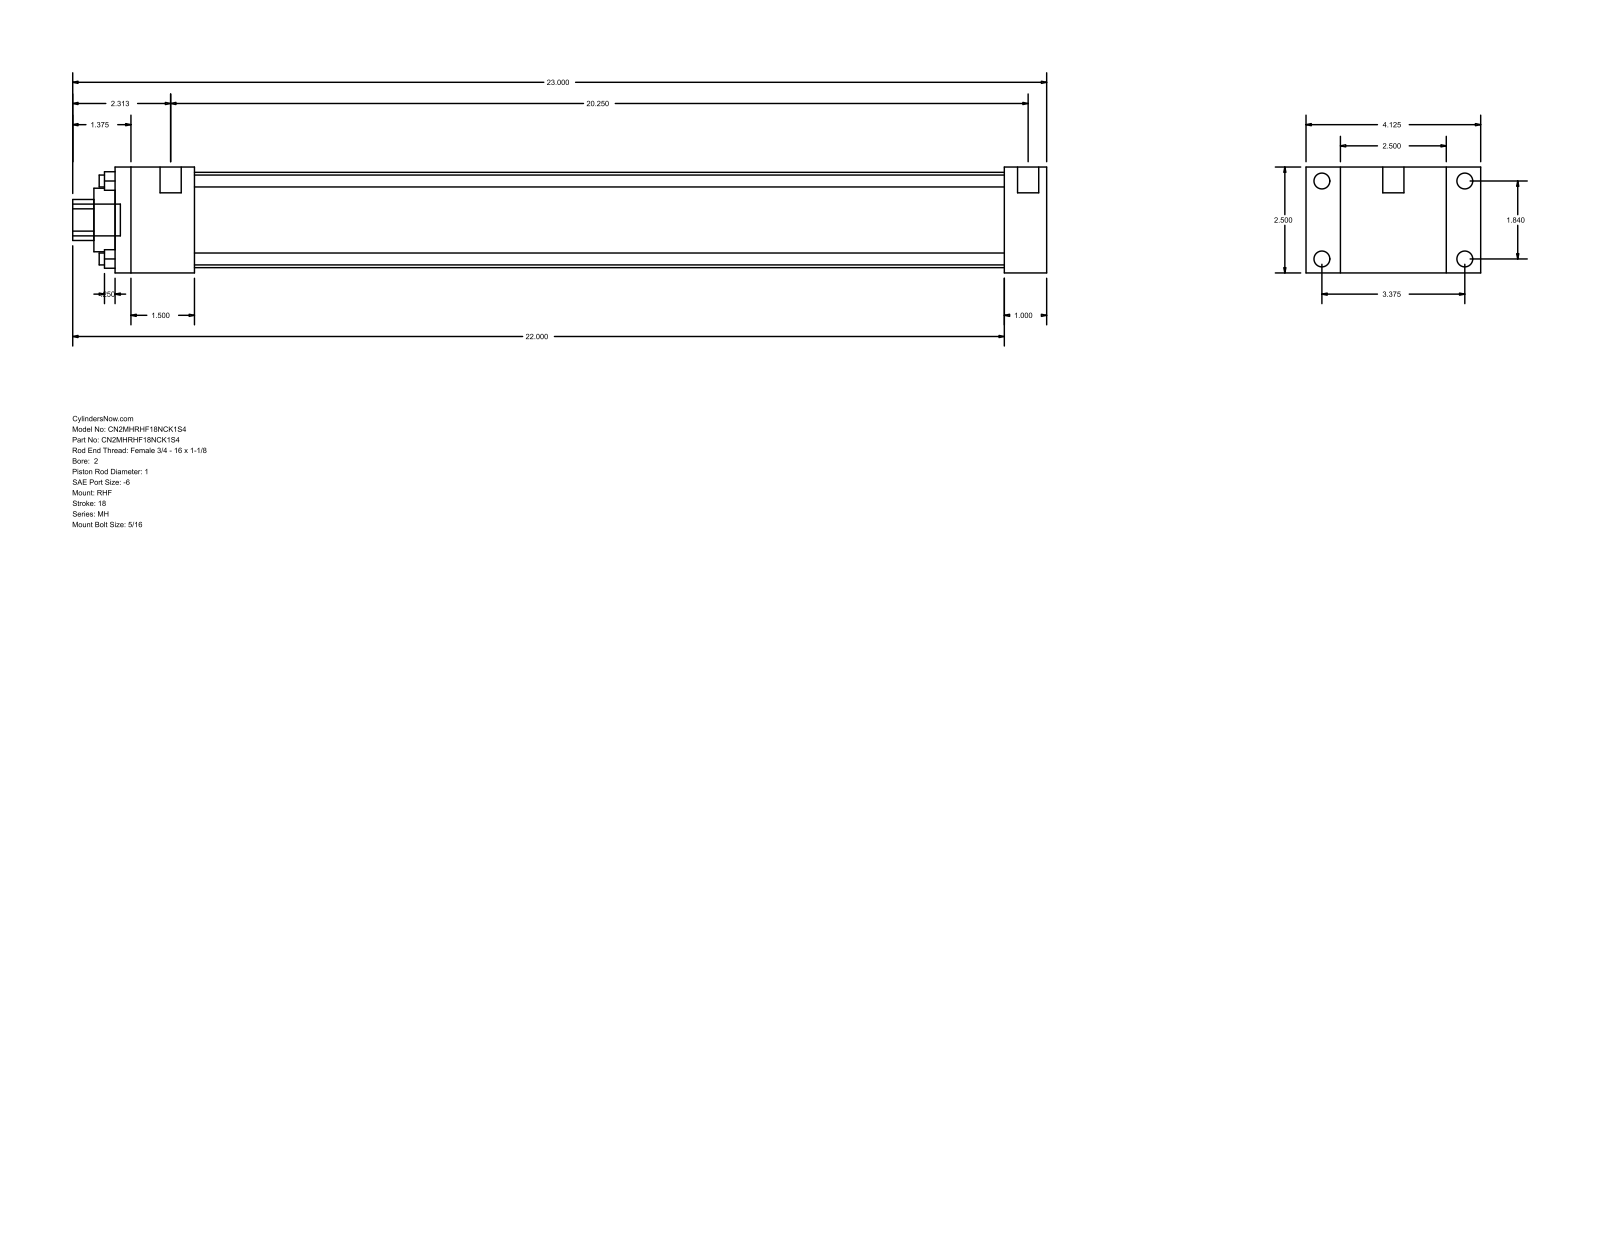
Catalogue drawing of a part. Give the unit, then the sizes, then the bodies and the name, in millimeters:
Units: millimetres
Overall size (bounding box): 584.2 × 104.78 × 63.5
Round holes (diameter × count): ⌀7.14 ×4, ⌀25.4 ×1, ⌀38.1 ×1, ⌀57.15 ×1
Round bosses / shafts (diameter × count): ⌀9.53 ×4, ⌀5.56 ×4, ⌀12.7 ×2, ⌀19.05 ×1
Partial cylindrical surfaces — rounded edges, fillets, slot ends (radius × count): R12.29 ×1
Main face-to-face distances: 63.5, 25.4, 20.64, 84.14, 558.8, 533.4, 104.78, 47.63, 485.77, 511.17
Hole centre spacings: 33.05, 46.74, 66.1
Bodies: 0 solids, 88 faces (60 planar, 28 cylindrical, 0 other)
Part name (STEP PRODUCT): MH_RHF__0200_1
STEP written by: GSSL Pune (CONFIG_CONTROL_DESIGN)
